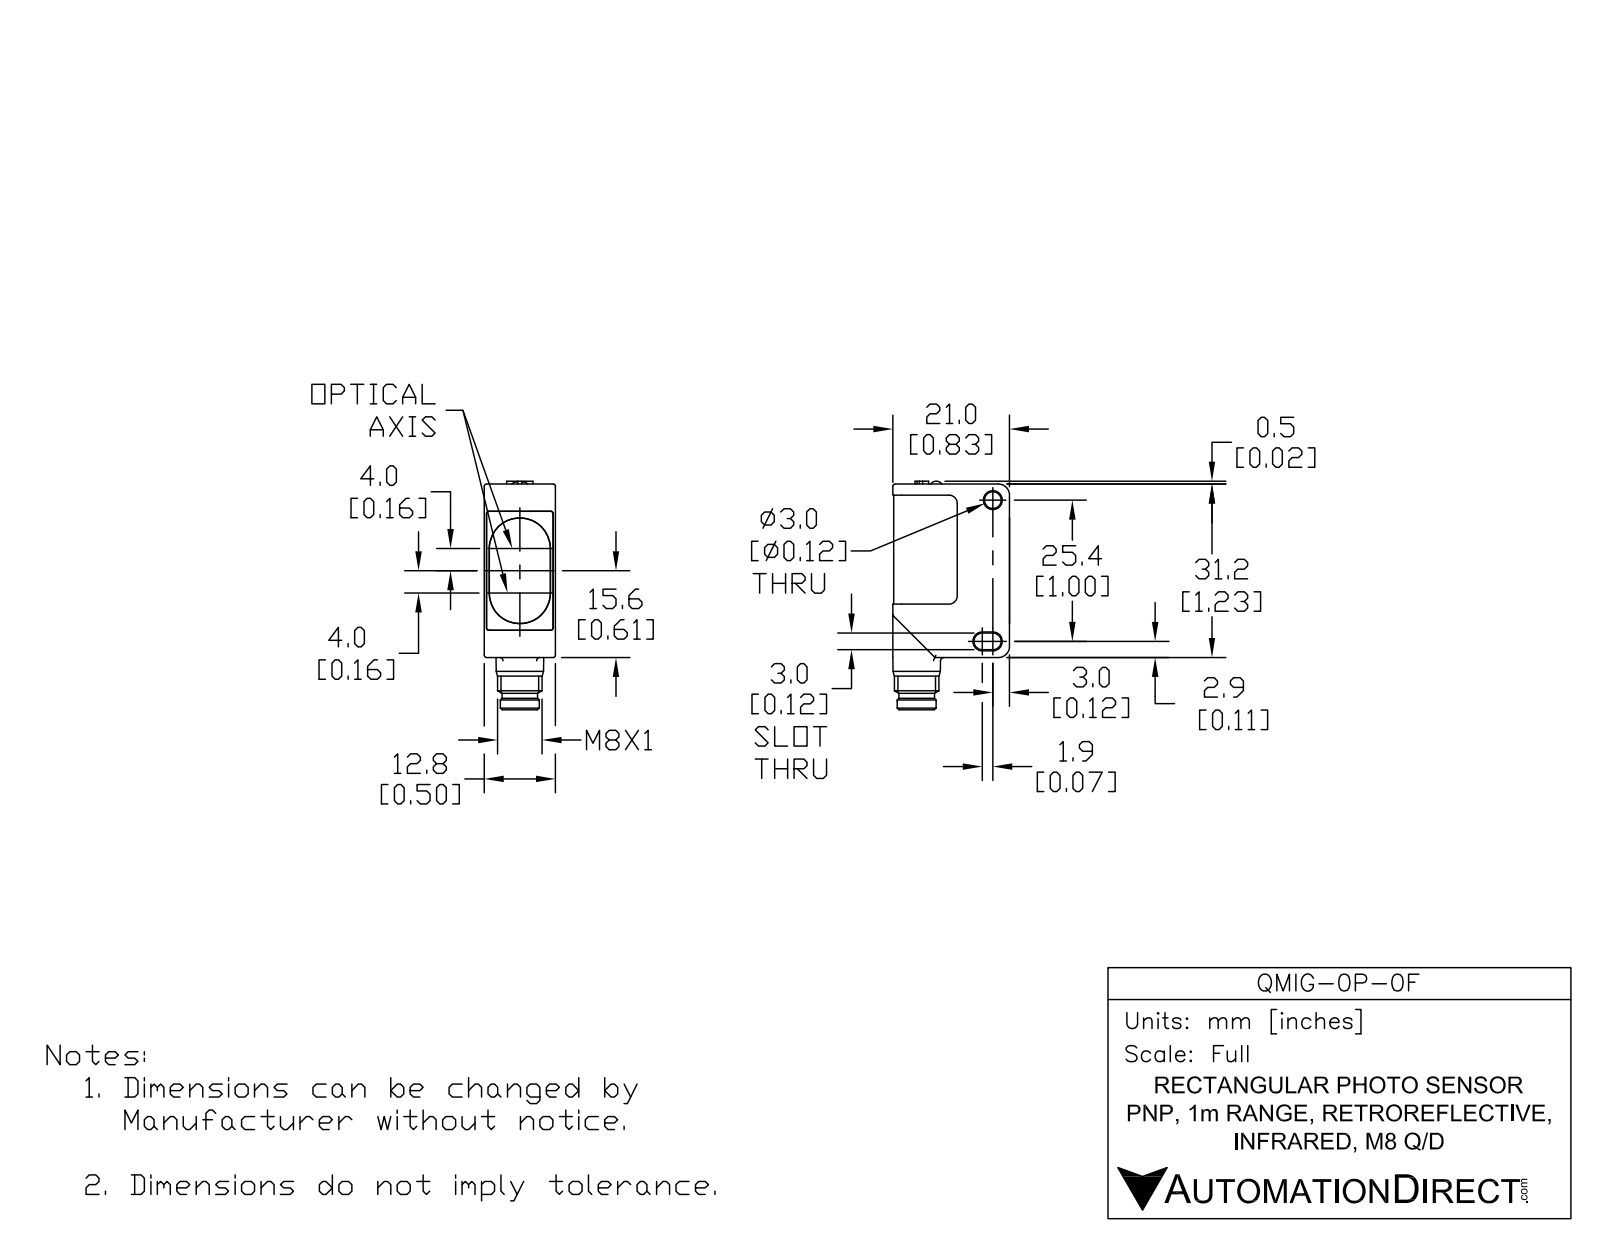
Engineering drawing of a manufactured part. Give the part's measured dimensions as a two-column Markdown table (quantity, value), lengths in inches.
| quantity | value |
| --- | --- |
| part name | QMIG-0P-0F |
| STEP written by | SolidWorks 2017 (AUTOMOTIVE_DESIGN) |
| units | inches |
| bodies | 7 solids, 272 faces (125 planar, 100 cylindrical, 47 other) |
| overall size | 1.619 × 0.827 × 0.504 |
| volume | 0.474 in³ |
| surface area | 7.749 in² |
| round holes (diameter × count) | 0.118 × 3, 0.228 × 1 |
| round bosses / shafts (diameter × count) | 0.039 × 4, 0.138 × 2, 0.315 × 1, 0.276 × 1, 0.252 × 1 |
| partial cylindrical surfaces (radius × count) | 0.016 × 10, 0.02 × 9, 0.059 × 6, 0.024 × 4, 0.039 × 4, 0.006 × 2, 0.044 × 2, 0.065 × 2 |
| main face-to-face distances | 0.498, 0.02, 0.504, 0.11, 0.016, 0.492, 0.488, 0.482, 0.059, 0.711 |
| hole center spacings | 0.04, 0.205, 0.245 |
